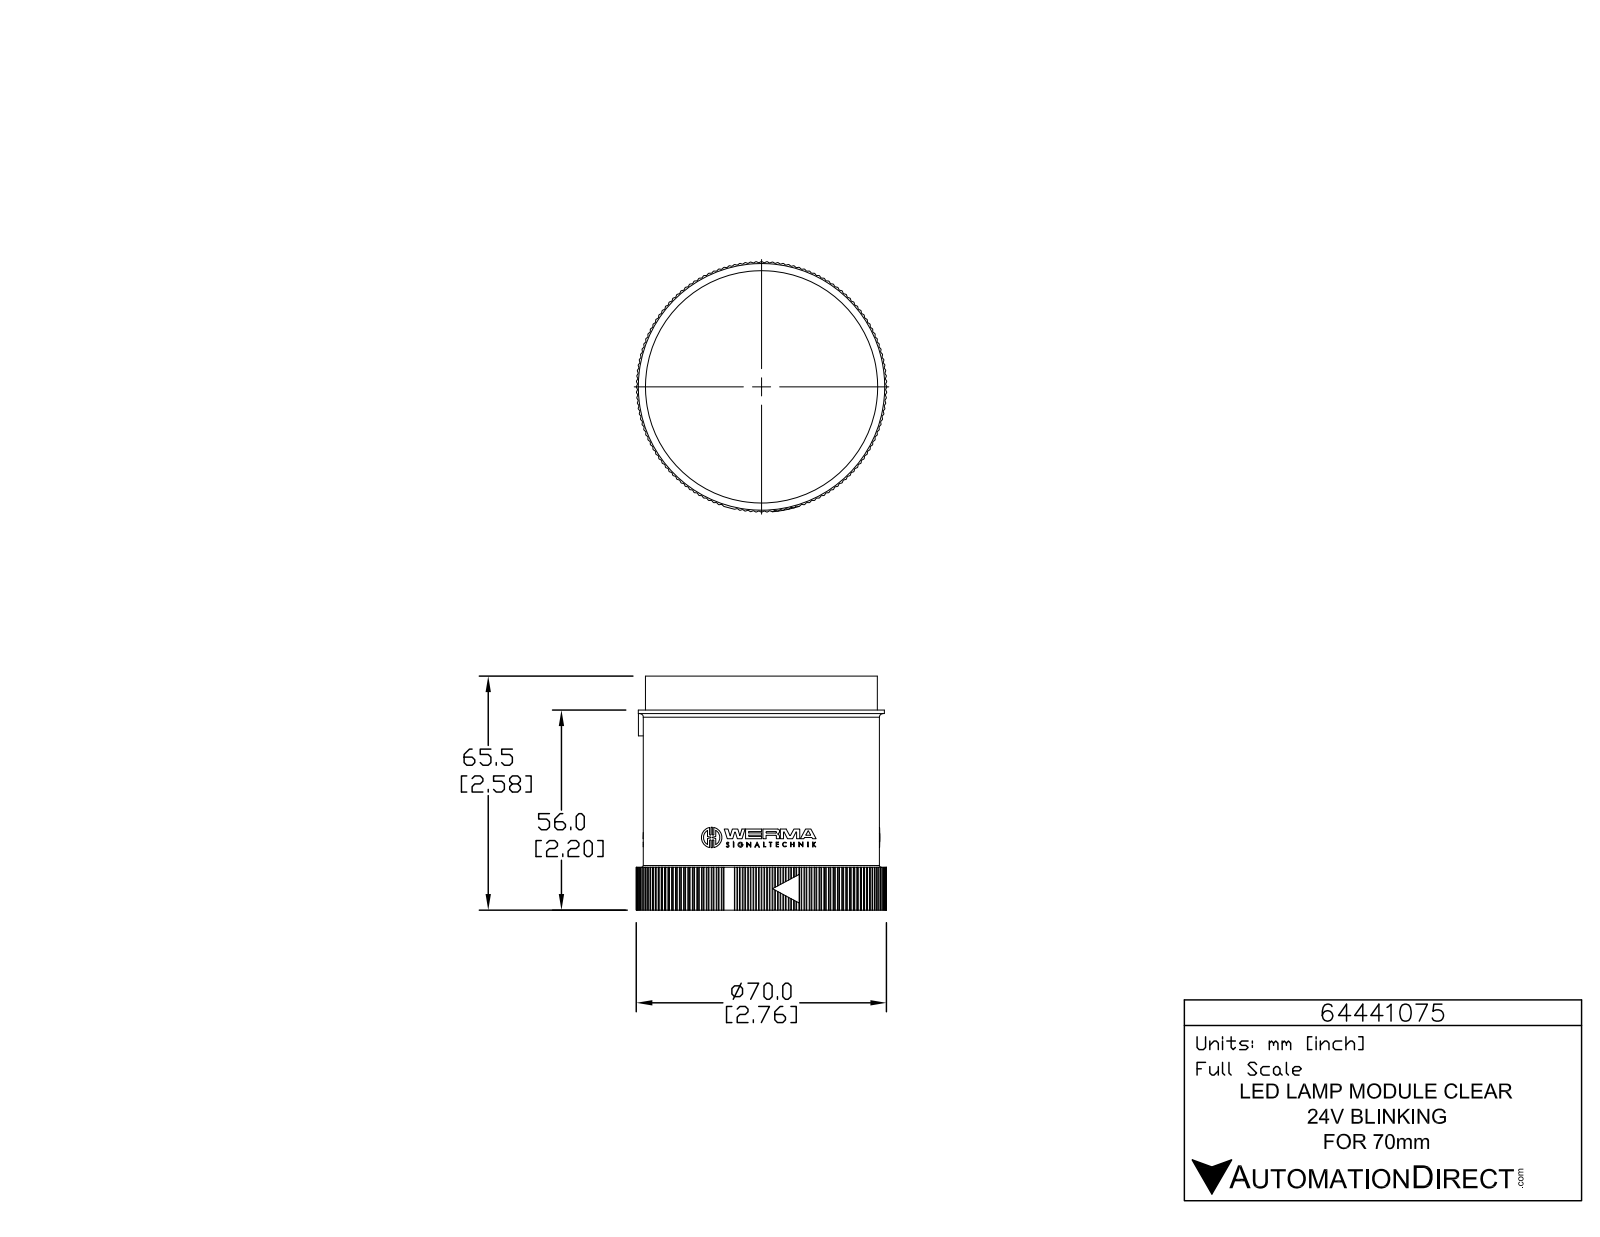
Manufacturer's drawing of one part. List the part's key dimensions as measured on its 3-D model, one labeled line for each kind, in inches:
Part name (STEP PRODUCT): 64441075
STEP written by: SolidWorks 2015 (AUTOMOTIVE_DESIGN)
Units: inches
Bodies: 1 solid, 1400 faces (832 planar, 563 cylindrical, 5 other)
Overall size (bounding box): 2.762 × 2.762 × 2.579
Volume: 12.02 in³ · Surface area: 37.48 in²
Round holes (diameter × count): ⌀0.039 ×3, ⌀2.575 ×1
Round bosses / shafts (diameter × count): ⌀0.226 ×3, ⌀0.056 ×3, ⌀2.717 ×1, ⌀2.606 ×1, ⌀2.559 ×1
Partial cylindrical surfaces — rounded edges, fillets, slot ends (radius × count): R0.008 ×285, R0.008 ×6, R0.008 ×6, R0.008 ×6, R0.131 ×6, R0.004 ×3, R0.005 ×3, R0.008 ×3
Main face-to-face distances: 2.201, 2.451, 0.378, 2.579, 2.205, 1.827, 0.374, 2.452, 0.472, 0.094
